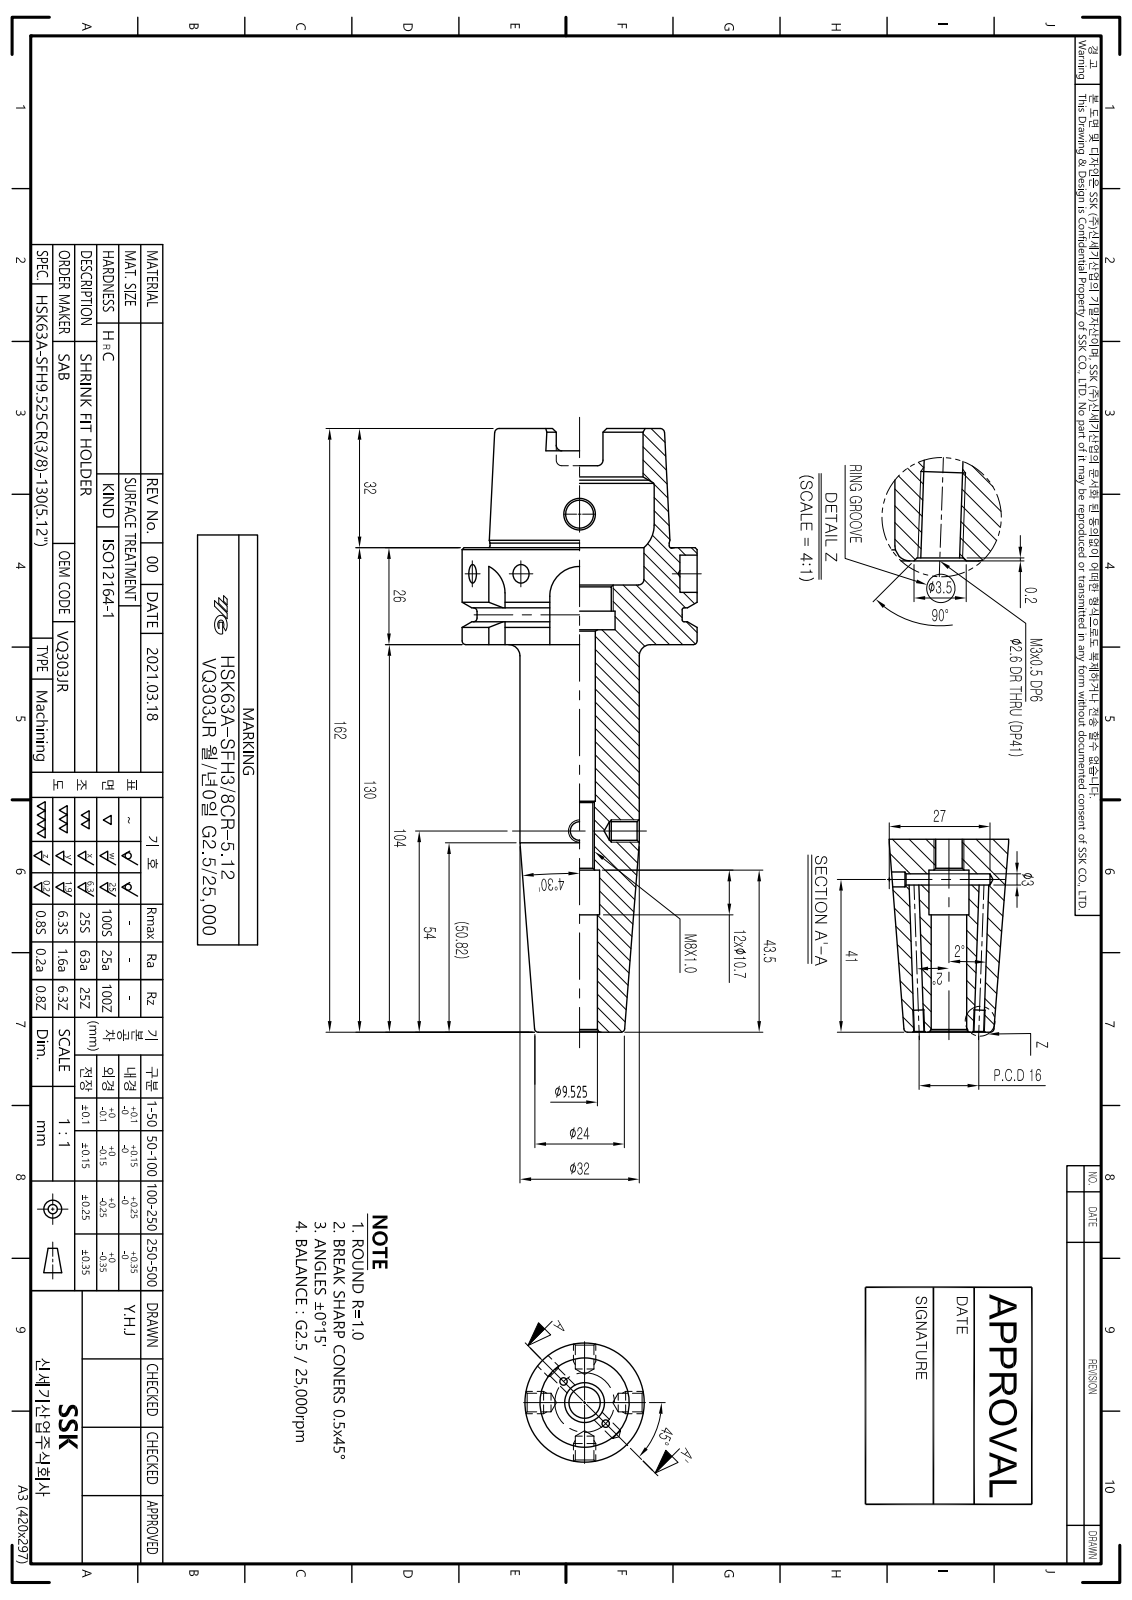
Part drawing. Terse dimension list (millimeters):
name: LO-HSK63A-SFH9.525CR-130
written by: Autodesk Inventor 2022 (AUTOMOTIVE_DESIGN)
unit: mm
bodies: 1 solid, 121 faces (42 planar, 36 cylindrical, 43 other)
size: 162 × 63 × 63
volume: 149 160 mm³; area: 35 148 mm²
holes: 2× ⌀2.46, 1× ⌀6.92, 1× ⌀7.5, 1× ⌀8.4, 1× ⌀9.53, 1× ⌀10, 1× ⌀10.7, 1× ⌀16.92, 1× ⌀19, 1× ⌀34, 1× ⌀40
bosses: 1× ⌀63, 1× ⌀55, 1× ⌀48.04, 1× ⌀32
rounds: 6× R1.5, 4× R2.88, 4× R8
face distances: 26, 10, 16, 32, 42, 58, 53, 22, 4, 12
